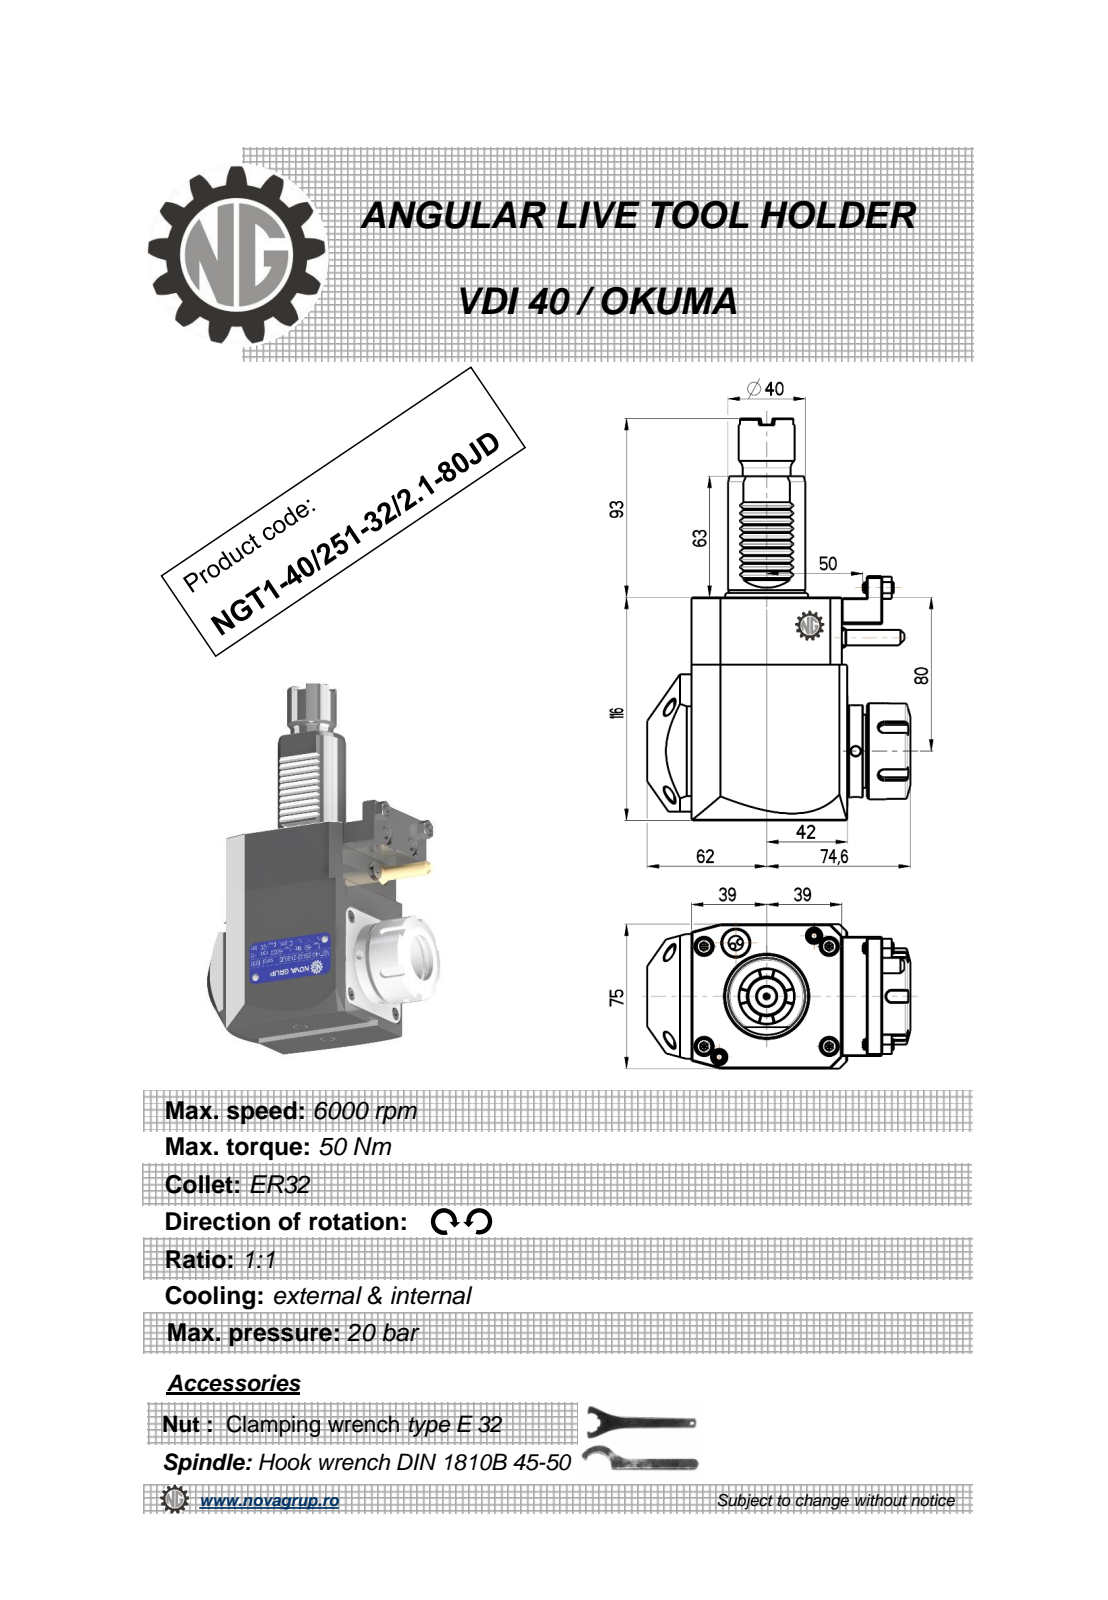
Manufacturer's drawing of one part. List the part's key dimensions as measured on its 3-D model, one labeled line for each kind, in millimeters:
Part name (STEP PRODUCT): NGT1_40_251_32_2_1_80JD
STEP written by: PRO/ENGINEER BY PARAMETRIC TECHNOLOGY CORPORATION, 2010280 (CONFIG_CONTROL_DESIGN)
Units: millimetres
Bodies: 1 solid, 456 faces (195 planar, 86 cylindrical, 175 other)
Overall size (bounding box): 209 × 136.6 × 76.6
Volume: 922 787 mm³ · Surface area: 75 215 mm²
Round holes (diameter × count): ⌀5 ×3, ⌀3 ×1, ⌀27 ×1
Round bosses / shafts (diameter × count): ⌀6 ×2, ⌀50 ×1, ⌀48 ×1, ⌀41 ×1, ⌀40 ×1, ⌀29 ×1, ⌀25 ×1, ⌀10 ×1
Partial cylindrical surfaces — rounded edges, fillets, slot ends (radius × count): R0.3 ×10, R0.31 ×10, R0.2 ×6, R3 ×5, R0.5 ×1, R10 ×1, R40 ×1
Main face-to-face distances: 75, 116, 81, 0.5, 18, 21, 80.8, 10, 14, 99
Hole centre spacings: 61.13
